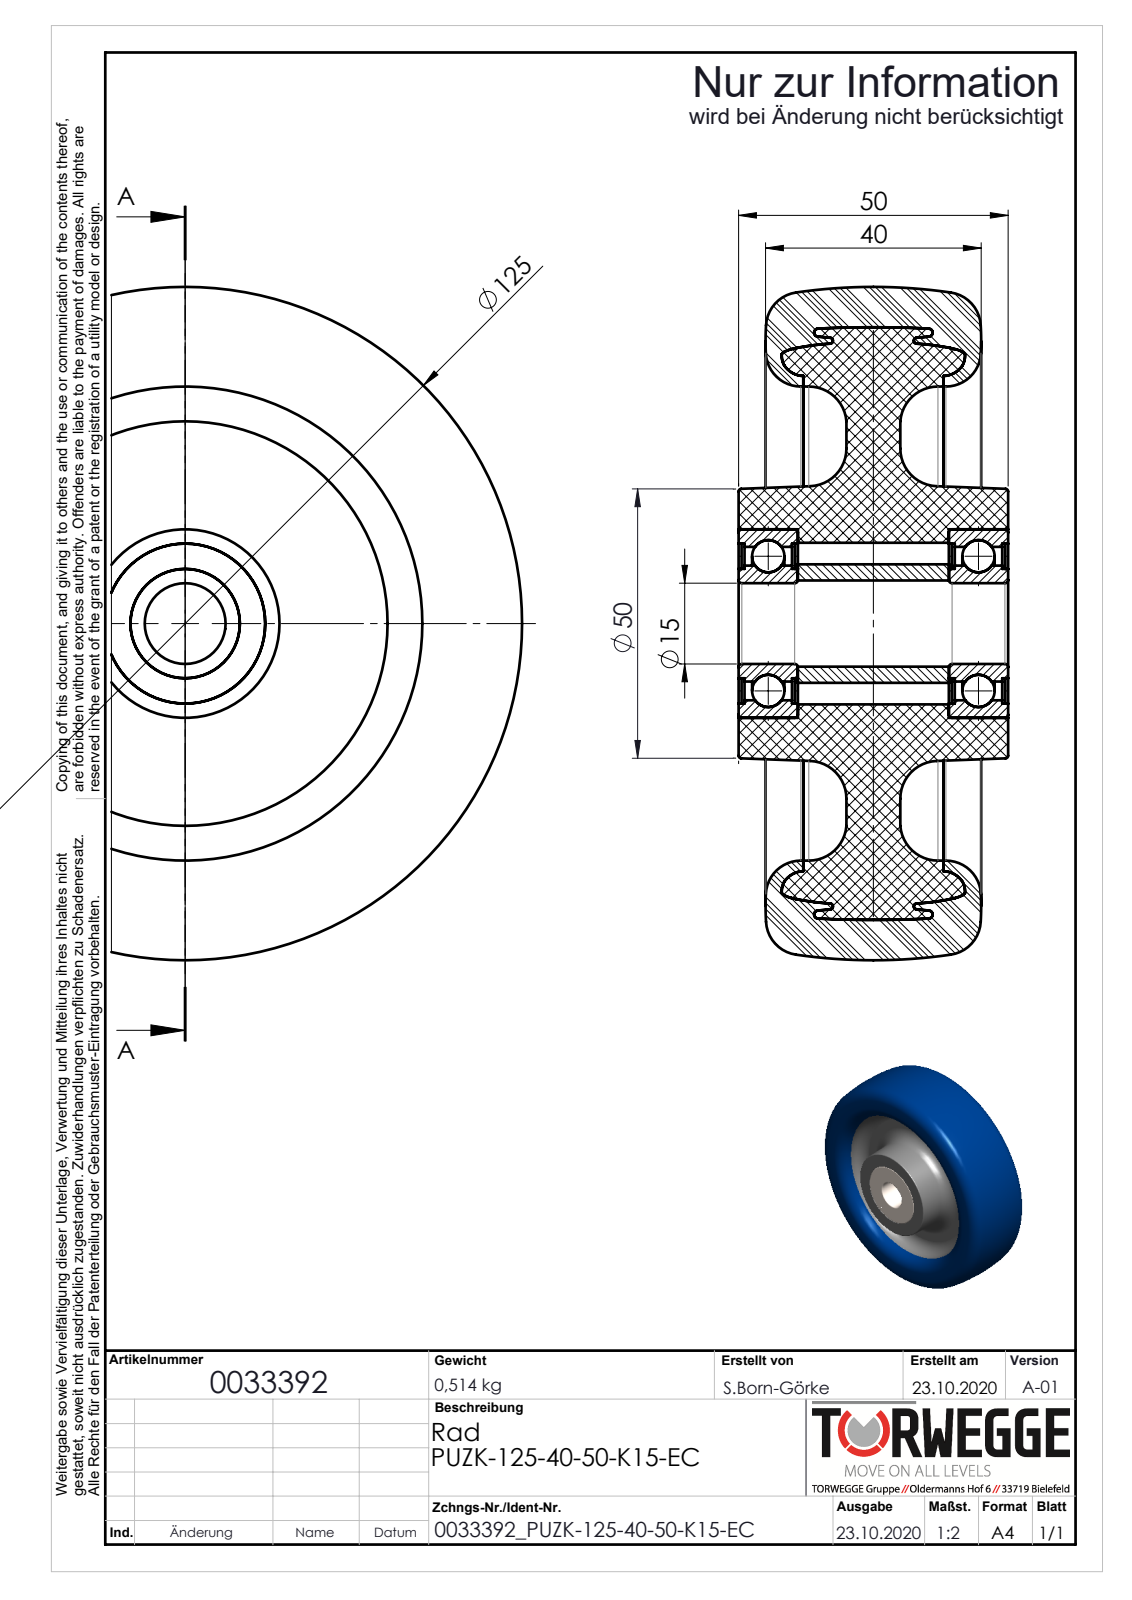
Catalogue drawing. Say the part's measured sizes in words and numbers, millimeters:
The part is named "0033392". Its 3-D file was written by "SolidWorks 2018 (AUTOMOTIVE_DESIGN)". It is 12 solids with 170 faces: 32 planar, 70 cylindrical and 68 other. Overall it measures 125 by 125 by 50 millimeters. Its volume is 356 118 cubic millimeters and its surface area 70 120 square millimeters. Round holes: 1 of diameter 15, 1 of diameter 16, 1 of diameter 20.3, 1 of diameter 28.48, 1 of diameter 29.7, 1 of diameter 30, 1 of diameter 35, 1 of diameter 88. Round bosses or shafts: 1 of diameter 22, 1 of diameter 21.52. The main face-to-face distances are 39, 20, 30, 11, 9, 19, 0.55, 50, 10.45, 9.9.
